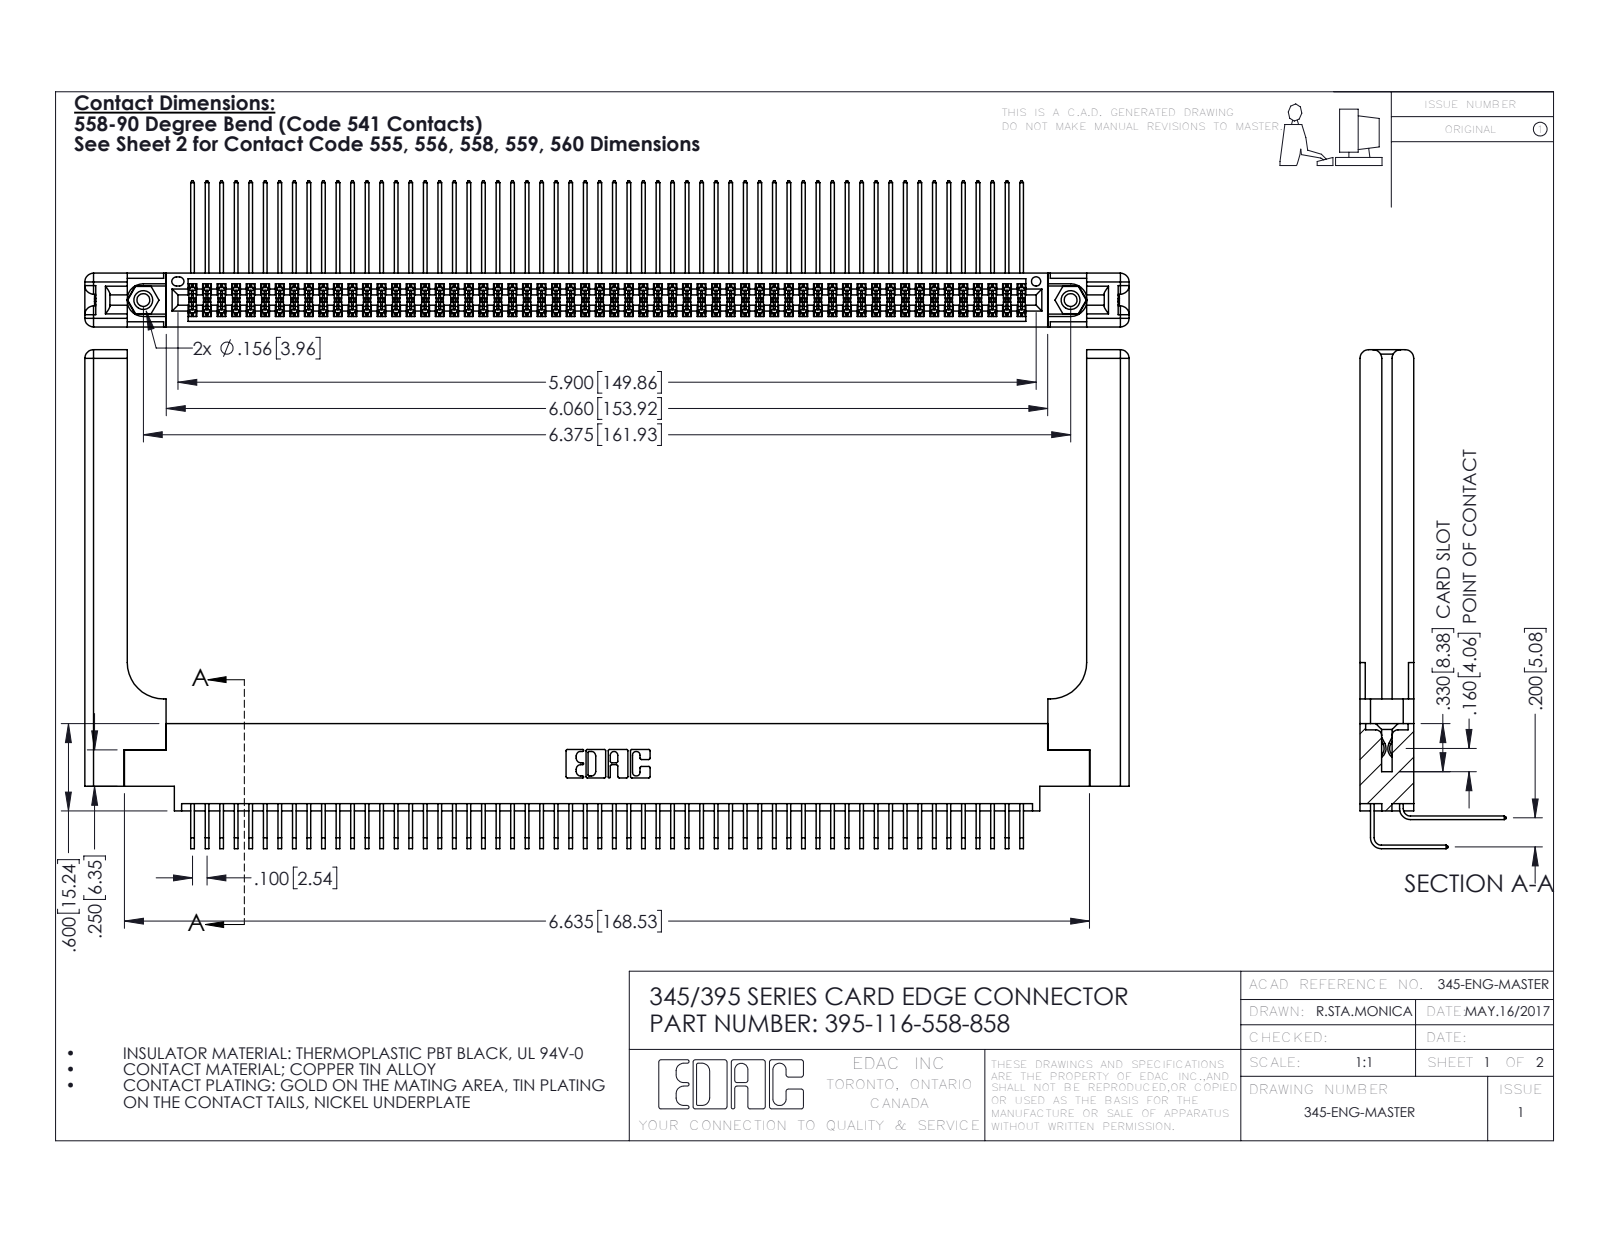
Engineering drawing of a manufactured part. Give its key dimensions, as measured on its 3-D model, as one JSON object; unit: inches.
{"part_name": "345-292-001_558 559 Tail - 1; 345-292-001_558 Tail - 2; 345-220-058_345-220-058; 395-116-558-858 (+2 more)", "step_written_by": "SolidWorks 2016 (CONFIG_CONTROL_DESIGN)", "units": "inches", "bodies": {"solids": 121, "faces": 6418, "planar": 4292, "cylindrical": 2066, "other": 60}, "overall_size": [7.179, 3.429, 1.005], "volume_in3": 1.641, "surface_area_in2": 55.62, "round_holes": [[0.089, 2], [0.125, 2], [0.156, 2], [0.064, 1]], "round_bosses_or_shafts": [[0.155, 2]], "partial_cylinders_radius": [[0.006, 174], [0.01, 22], [0.06, 16], [0.007, 6], [0.031, 6], [0.026, 3], [0.014, 2], [0.019, 2]], "face_to_face_distances": [0.072, 0.298, 0.37, 0.2, 0.098, 0.272, 0.025, 0.225, 0.175, 0.148], "hole_center_spacings": [0.27, 6.139, 6.375]}
